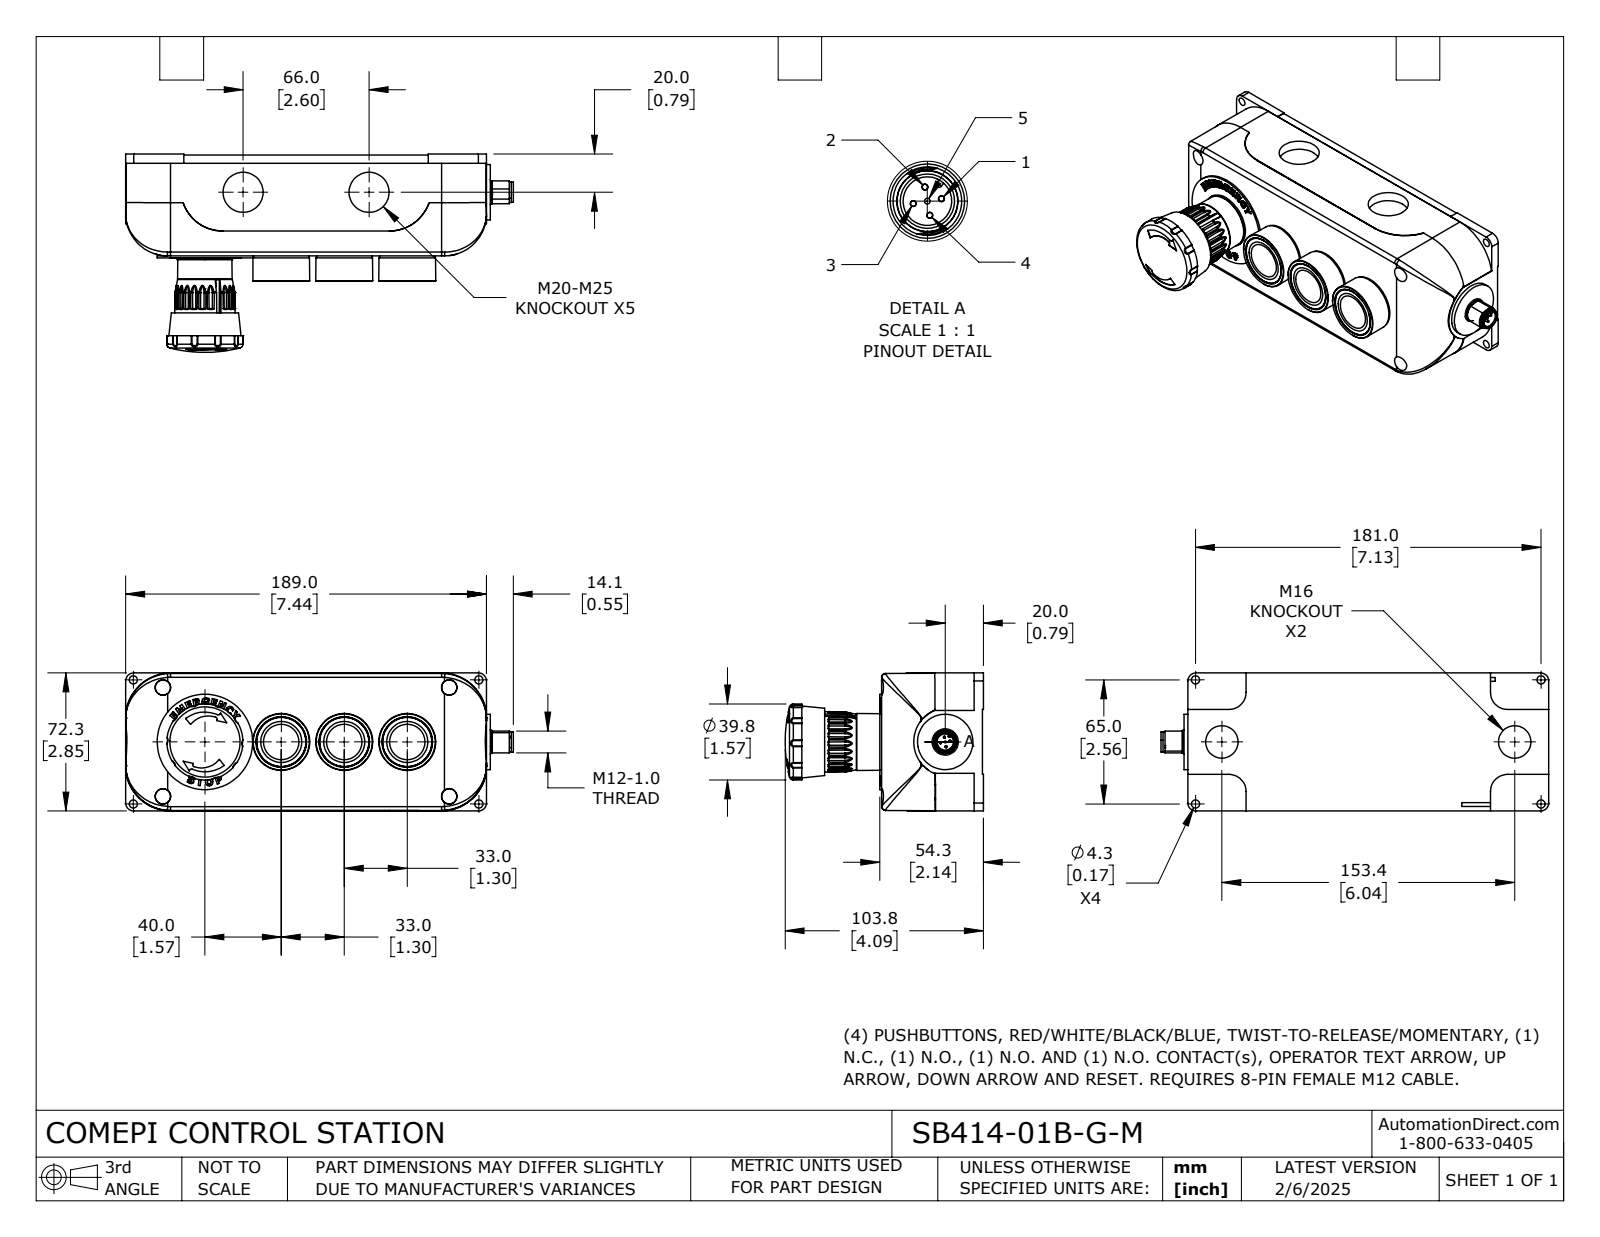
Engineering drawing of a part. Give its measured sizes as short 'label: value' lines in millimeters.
name: SB414-01B-G-M
written by: SolidWorks 2024 (CONFIG_CONTROL_DESIGN)
unit: mm
bodies: 18 solids, 1611 faces (559 planar, 396 cylindrical, 656 other)
size: 203 × 103.8 × 72.3
volume: 401 300 mm³; area: 147 200 mm²
holes: 4× ⌀1, 4× ⌀1.7, 4× ⌀2.2, 4× ⌀4.3, 4× ⌀18.1, 3× ⌀13.5, 3× ⌀21, 3× ⌀21.7, 2× ⌀17, 1× ⌀1.3, 1× ⌀8.5, 1× ⌀22
bosses: 5× ⌀29, 5× ⌀1, 4× ⌀2.2, 4× ⌀1.7, 3× ⌀25.8, 3× ⌀19, 3× ⌀18.5, 3× ⌀16
rounds: 28× R1, 18× R0.5, 10× R6.8, 8× R0.2, 8× R0.3, 4× R0.9, 4× R2, 4× R4
face distances: 52.8, 2.5, 50.3, 13, 39.8, 37.3, 60.8, 66.5, 1, 15
hole spacings: 3.5, 35.3, 49.6, 147.1, 170.3, 2.5, 2.5, 5
